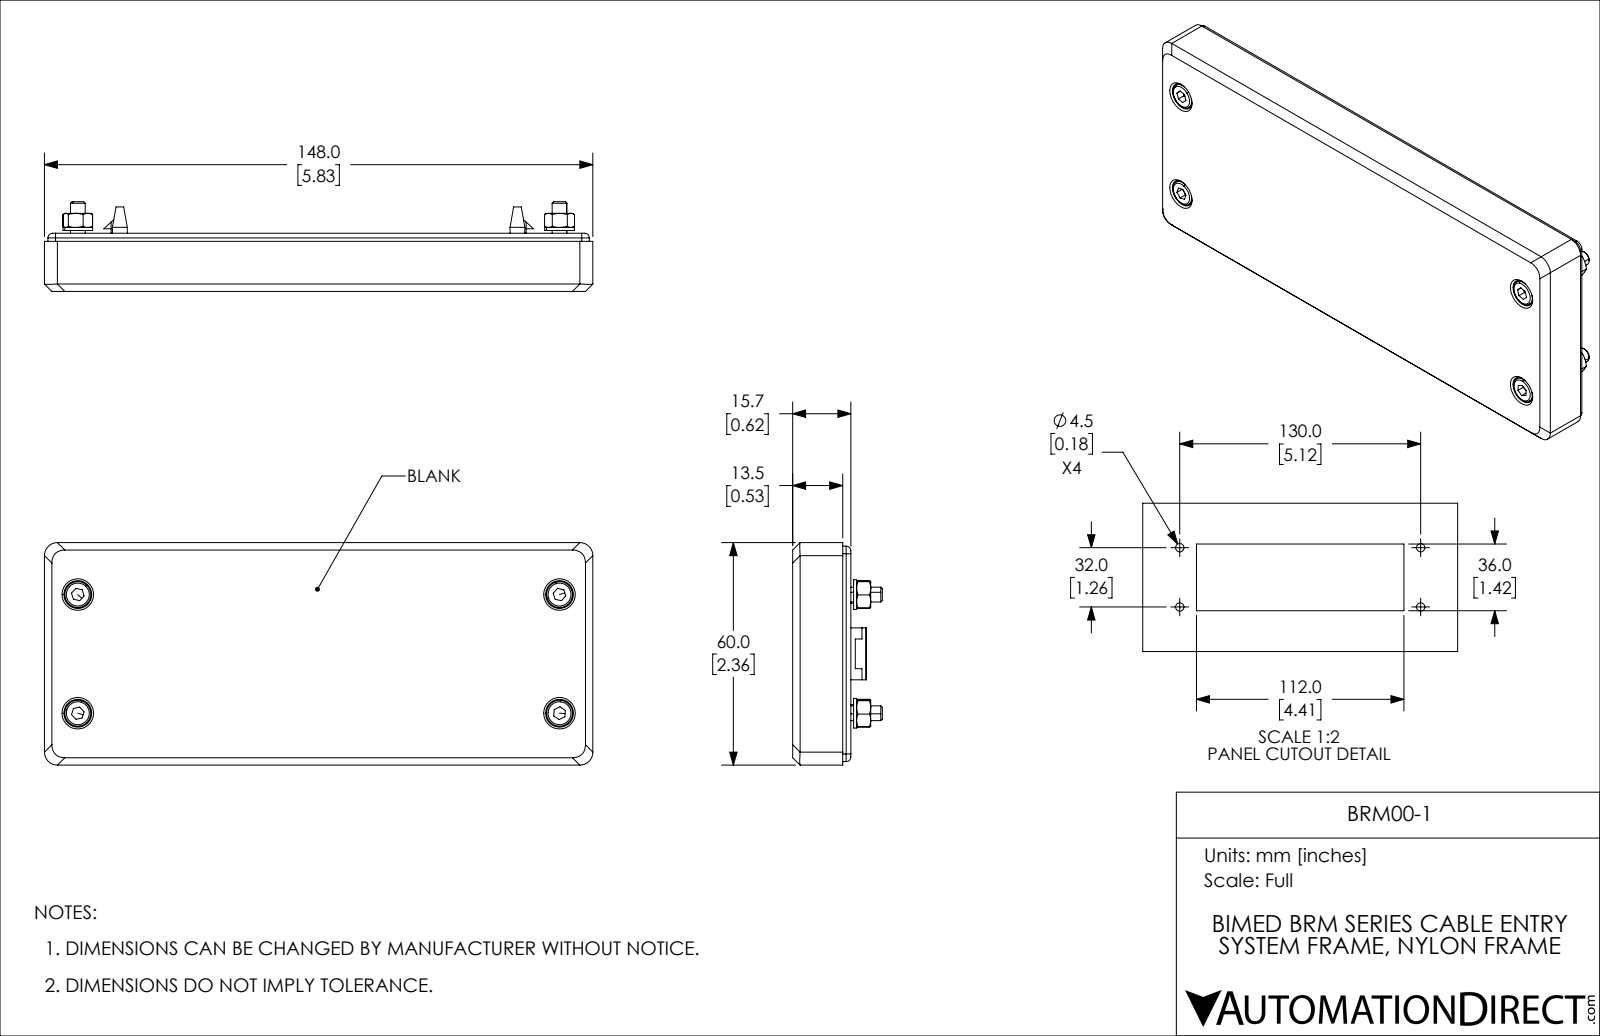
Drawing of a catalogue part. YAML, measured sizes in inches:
part_name: "BRM00-1"
step_written_by: "SolidWorks 2021 (CONFIG_CONTROL_DESIGN)"
units: inches
bodies: {solids: 17, faces: 1009, planar: 267, cylindrical: 400, other: 342}
overall_size: [5.827, 2.362, 0.953]
volume: 3.934
surface_area: 88.47
round_holes:
  - {diameter: 0.472, count: 23}
  - {diameter: 0.11, count: 14}
  - {diameter: 0.098, count: 4}
  - {diameter: 0.128, count: 4}
  - {diameter: 0.169, count: 4}
  - {diameter: 0.177, count: 4}
  - {diameter: 0.295, count: 4}
round_bosses_or_shafts:
  - {diameter: 0.098, count: 16}
  - {diameter: 0.157, count: 8}
  - {diameter: 0.315, count: 4}
  - {diameter: 0.276, count: 4}
partial_cylinders:
  - {radius: 0.039, count: 60}
  - {radius: 0.049, count: 8}
  - {radius: 0.197, count: 8}
  - {radius: 0.02, count: 6}
  - {radius: 0.079, count: 4}
  - {radius: 0.081, count: 4}
  - {radius: 0.138, count: 4}
  - {radius: 0.195, count: 4}
face_to_face_distances: [0.098, 0.167, 0.228, 0.157, 2.195, 0.327, 0.386, 0.484, 2.028, 2.362]
hole_center_spacings: [1.732, 0.504, 0.447, 0.472, 0.591, 0.63, 0.702, 0.75]
